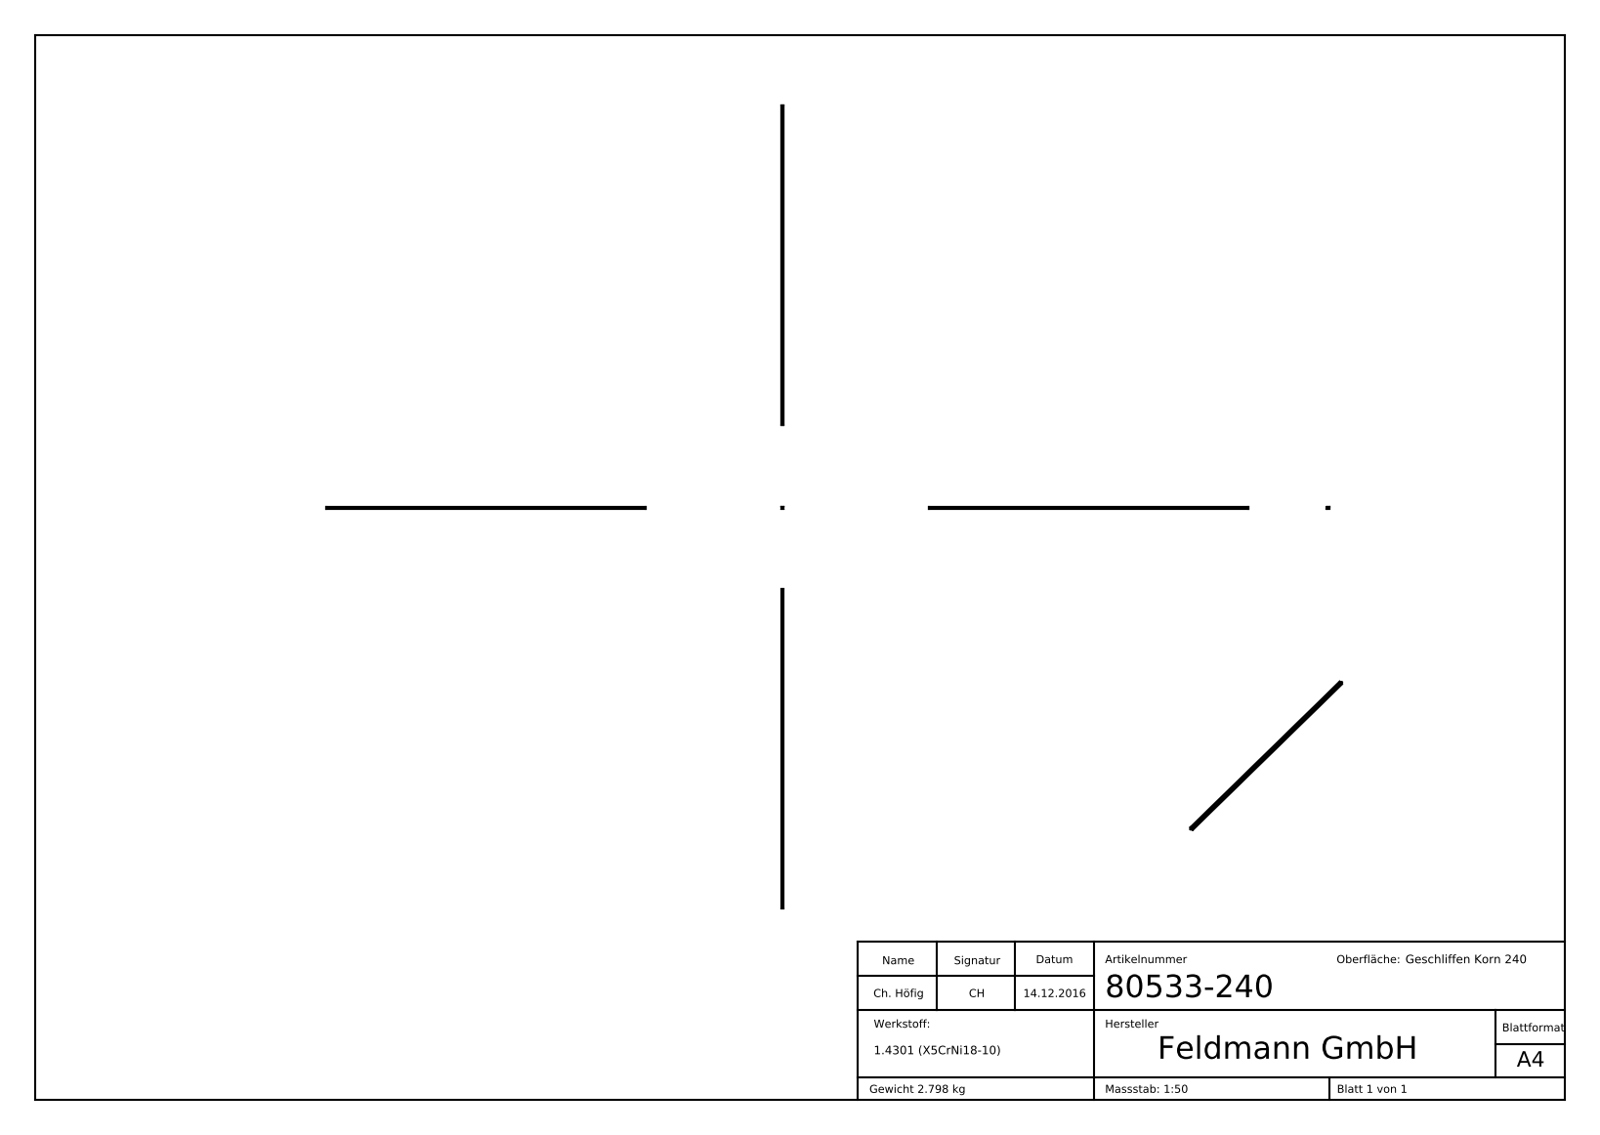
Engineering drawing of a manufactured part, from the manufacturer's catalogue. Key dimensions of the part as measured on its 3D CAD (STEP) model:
Part name (STEP PRODUCT): 80533-240
STEP written by: SolidWorks 2015 (CONFIG_CONTROL_DESIGN)
Units: millimetres
Bodies: 1 solid, 283 faces (151 planar, 6 cylindrical, 126 other)
Overall size (bounding box): 3000 × 24 × 20
Volume: 354 205 mm³ · Surface area: 364 522 mm²
Partial cylindrical surfaces — rounded edges, fillets, slot ends (radius × count): R0.5 ×4, R2 ×2
Main face-to-face distances: 2, 22, 20, 24, 18, 3000, 1.9, 20.1, 22.1, 8.75
